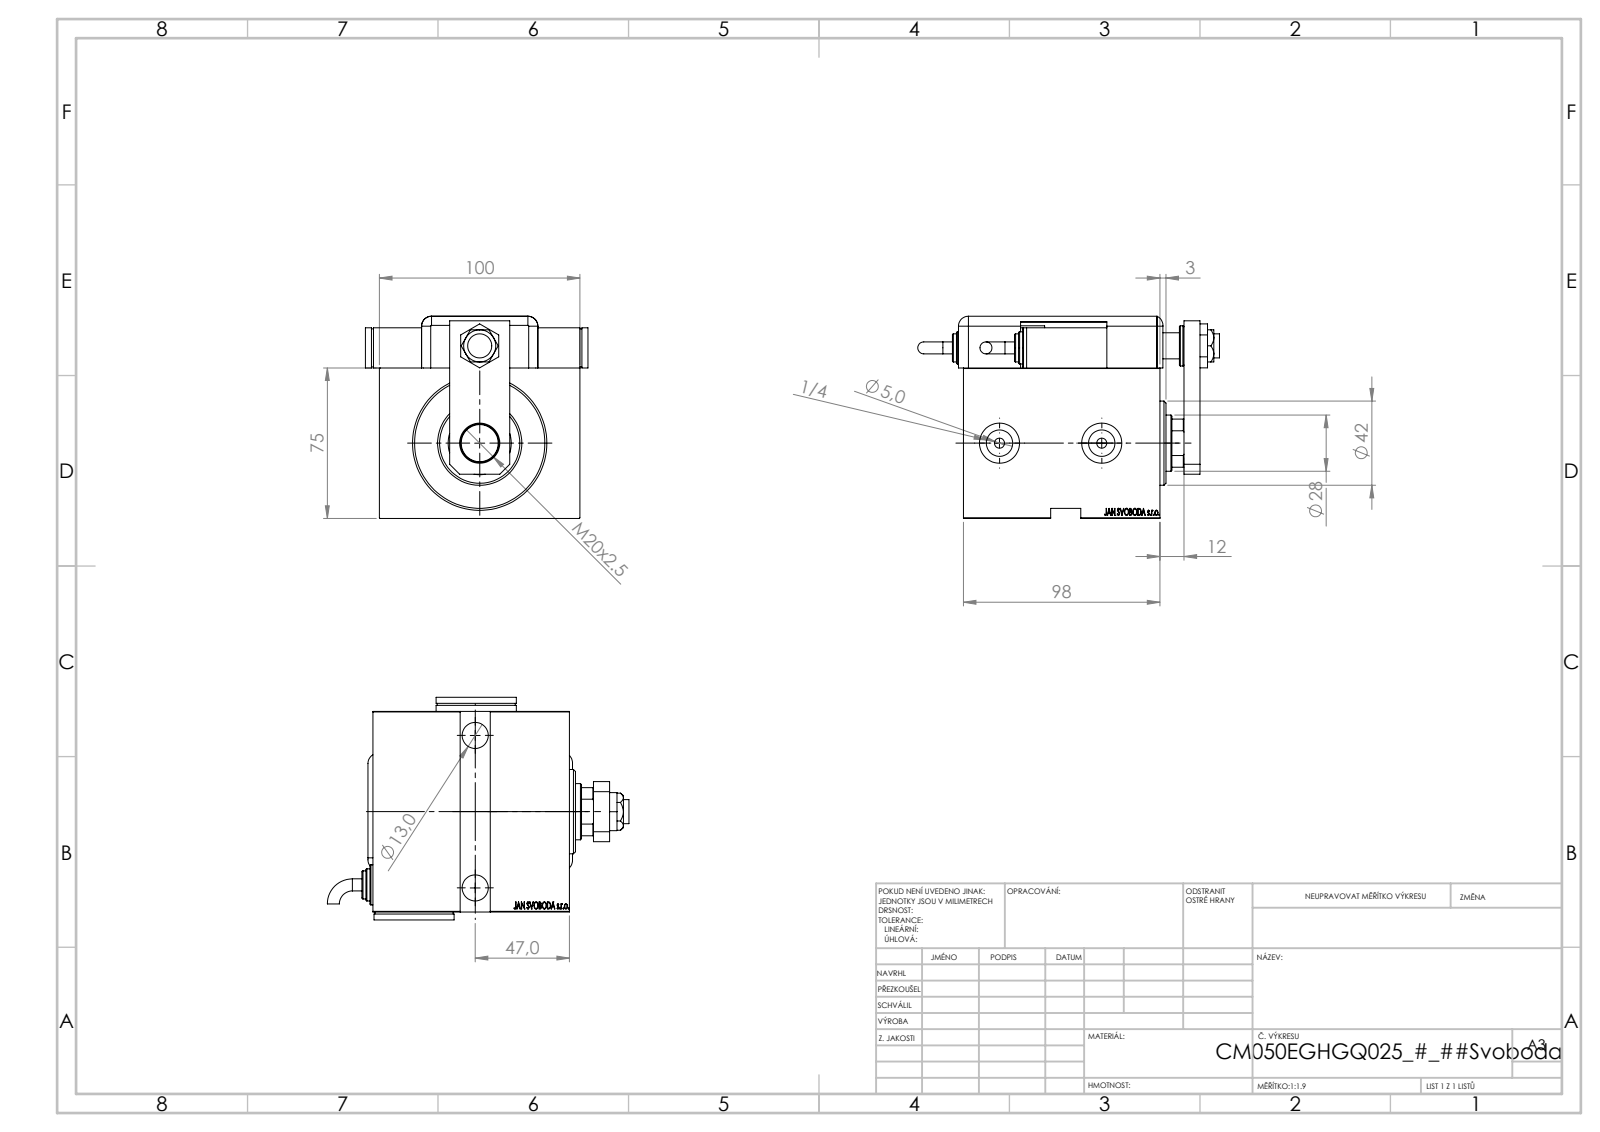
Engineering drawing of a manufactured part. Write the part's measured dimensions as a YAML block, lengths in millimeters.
part_name: "V450CM_E_VCP; SWITCH_Q_FRONT_BACK; NUT_D19; NUT_D13 (+7 more)"
step_written_by: "SolidWorks 2019 (CONFIG_CONTROL_DESIGN)"
units: millimeters
bodies: {solids: 13, faces: 1230, planar: 614, cylindrical: 99, other: 517}
overall_size: [150.46, 111, 100.8]
volume: 815618
surface_area: 152621
round_holes:
  - {diameter: 13, count: 3}
  - {diameter: 20, count: 3}
  - {diameter: 4, count: 2}
  - {diameter: 5, count: 2}
  - {diameter: 8, count: 2}
  - {diameter: 13.16, count: 2}
  - {diameter: 19, count: 2}
  - {diameter: 12, count: 1}
  - {diameter: 14, count: 1}
  - {diameter: 18.5, count: 1}
  - {diameter: 28, count: 1}
  - {diameter: 31.5, count: 1}
round_bosses_or_shafts:
  - {diameter: 20, count: 3}
  - {diameter: 16, count: 2}
  - {diameter: 14, count: 2}
  - {diameter: 6, count: 2}
  - {diameter: 52, count: 1}
  - {diameter: 42, count: 1}
partial_cylinders:
  - {radius: 5, count: 9}
  - {radius: 10, count: 1}
  - {radius: 13.5, count: 1}
face_to_face_distances: [3, 75, 98, 100, 14, 20, 79, 84, 100.8, 25.8]
hole_center_spacings: [47.2, 61.22, 20, 48.5, 51, 76]
